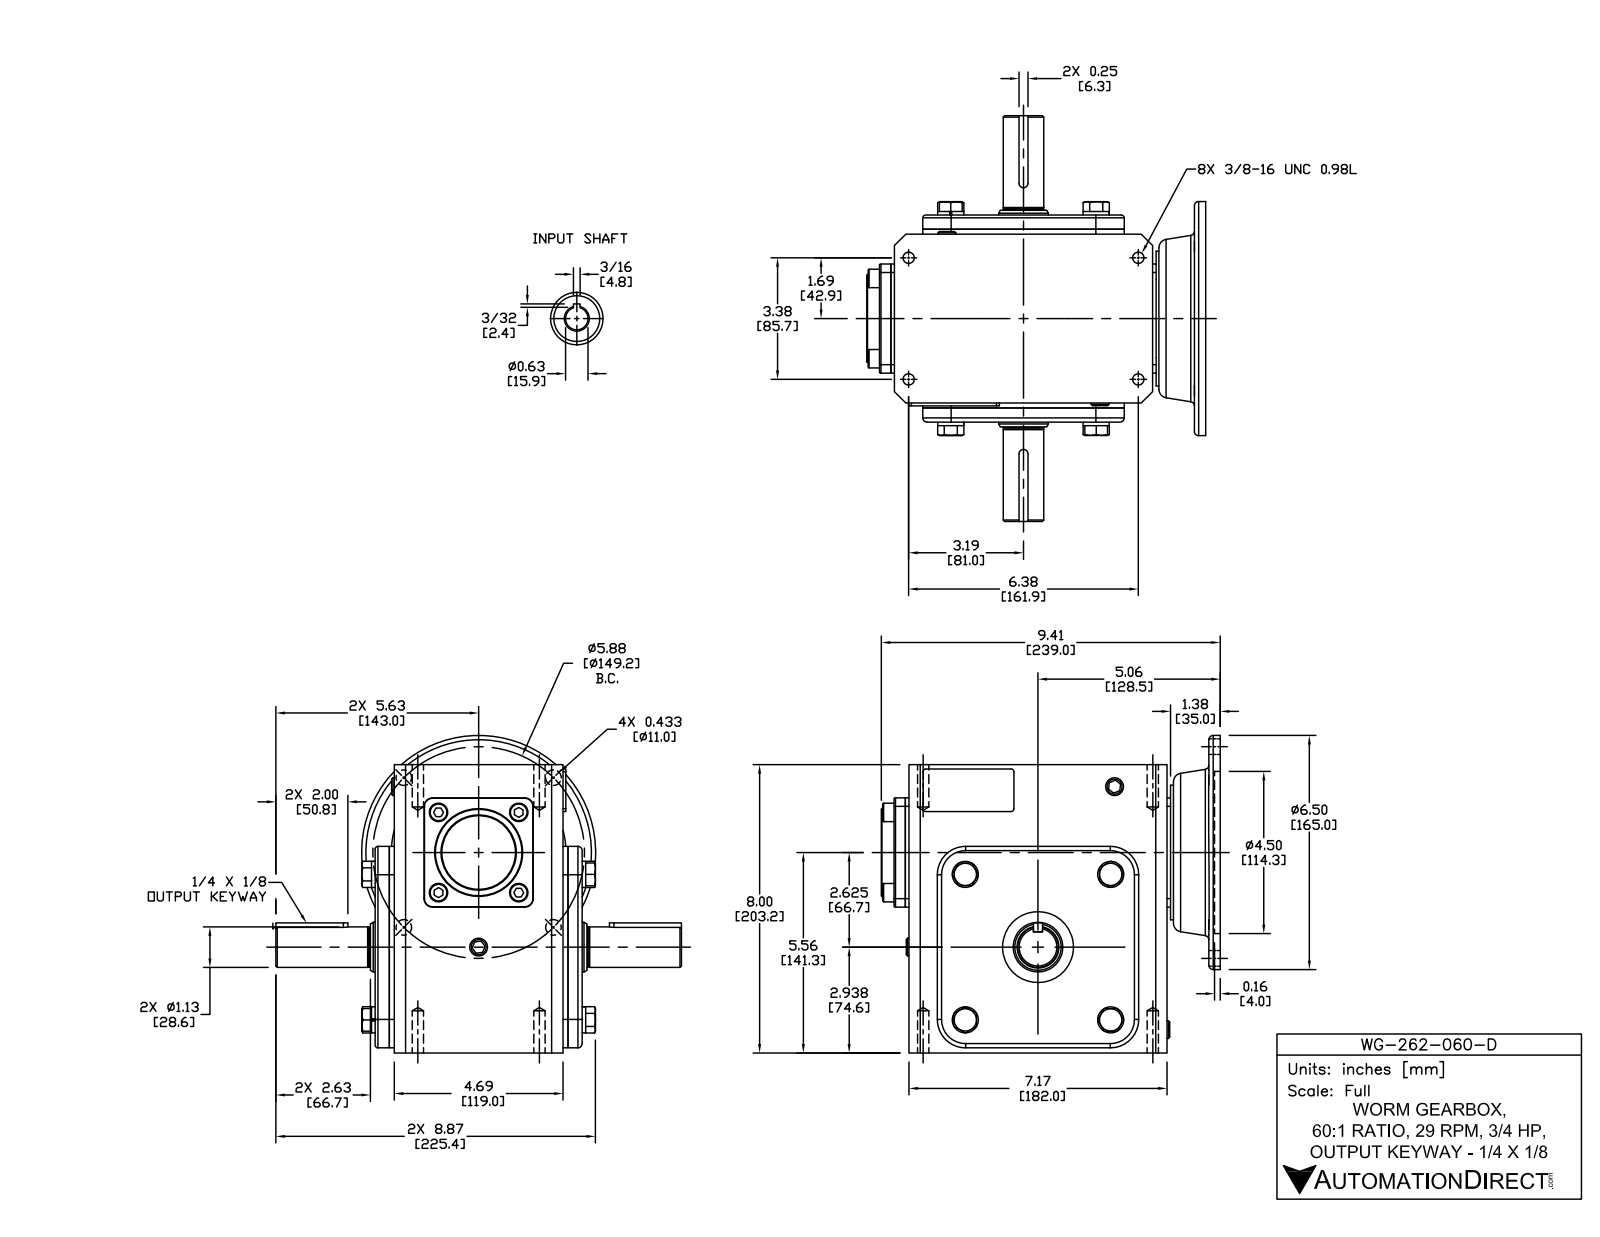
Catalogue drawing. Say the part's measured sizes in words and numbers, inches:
The part is named "WG-262-060-D". Its 3-D file was written by "SolidWorks 2015 (CONFIG_CONTROL_DESIGN)". It is 39 solids with 562 faces: 307 planar, 150 cylindrical and 105 other. Overall it measures 11.26 by 9.409 by 8.811 inches. Its volume is 322.1 cubic inches and its surface area 632.6 square inches. Round holes: 4 of diameter 0.313, 4 of diameter 0.406, 1 of diameter 0.591, 1 of diameter 0.625, 1 of diameter 1.181, 1 of diameter 1.378, 1 of diameter 1.457, 1 of diameter 1.969, 1 of diameter 3.819, 1 of diameter 4.5. Round bosses or shafts: 4 of diameter 0.724, 4 of diameter 0.512, 1 of diameter 6.496, 1 of diameter 2.441, 1 of diameter 2.047, 1 of diameter 1.142, 1 of diameter 1.125, 1 of diameter 1.113. Partial cylindrical surfaces (rounded edges, fillets, slot ends): 8 of radius 0.079, 8 of radius 0.118, 4 of radius 0.236, 4 of radius 0.787, 2 of radius 0.02, 2 of radius 0.039, 2 of radius 0.125. The main face-to-face distances are 4.961, 0.394, 5.354, 5.217, 0.531, 0.138, 4.823, 8, 0.098, 7.264. The hole center spacings are 2.937, 4.154, 2.148, 3.375, 5.14, 5.875, 6.375, 7.213.
